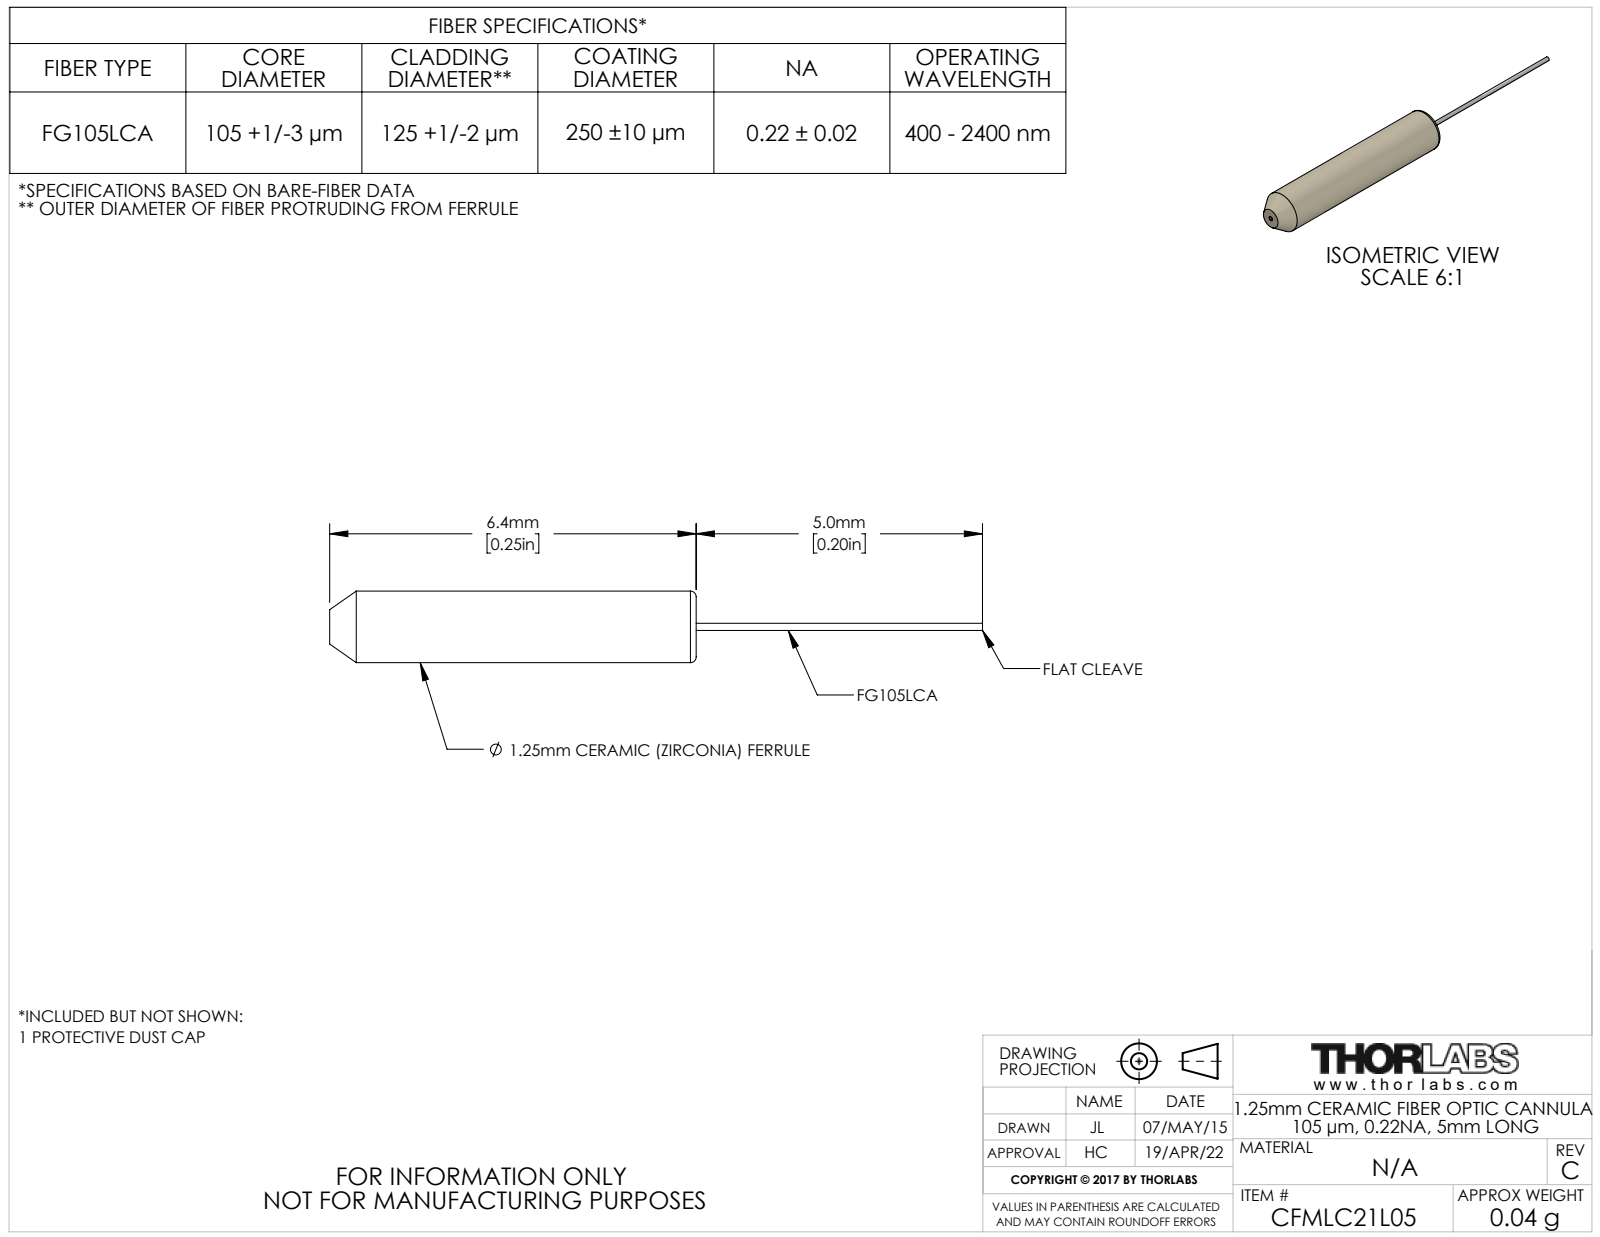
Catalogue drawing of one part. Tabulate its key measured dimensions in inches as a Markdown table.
| quantity | value |
| --- | --- |
| part name | TTN041720-E0W |
| STEP written by | SolidWorks 2014 (CONFIG_CONTROL_DESIGN) |
| units | inches |
| bodies | 2 solids, 18 faces (4 planar, 6 cylindrical, 8 other) |
| overall size | 0.449 × 0.049 × 0.049 |
| round bosses / shafts (diameter × count) | 0.049 × 1 |
| main face-to-face distances | 0.252, 0.449, 0.197 |
